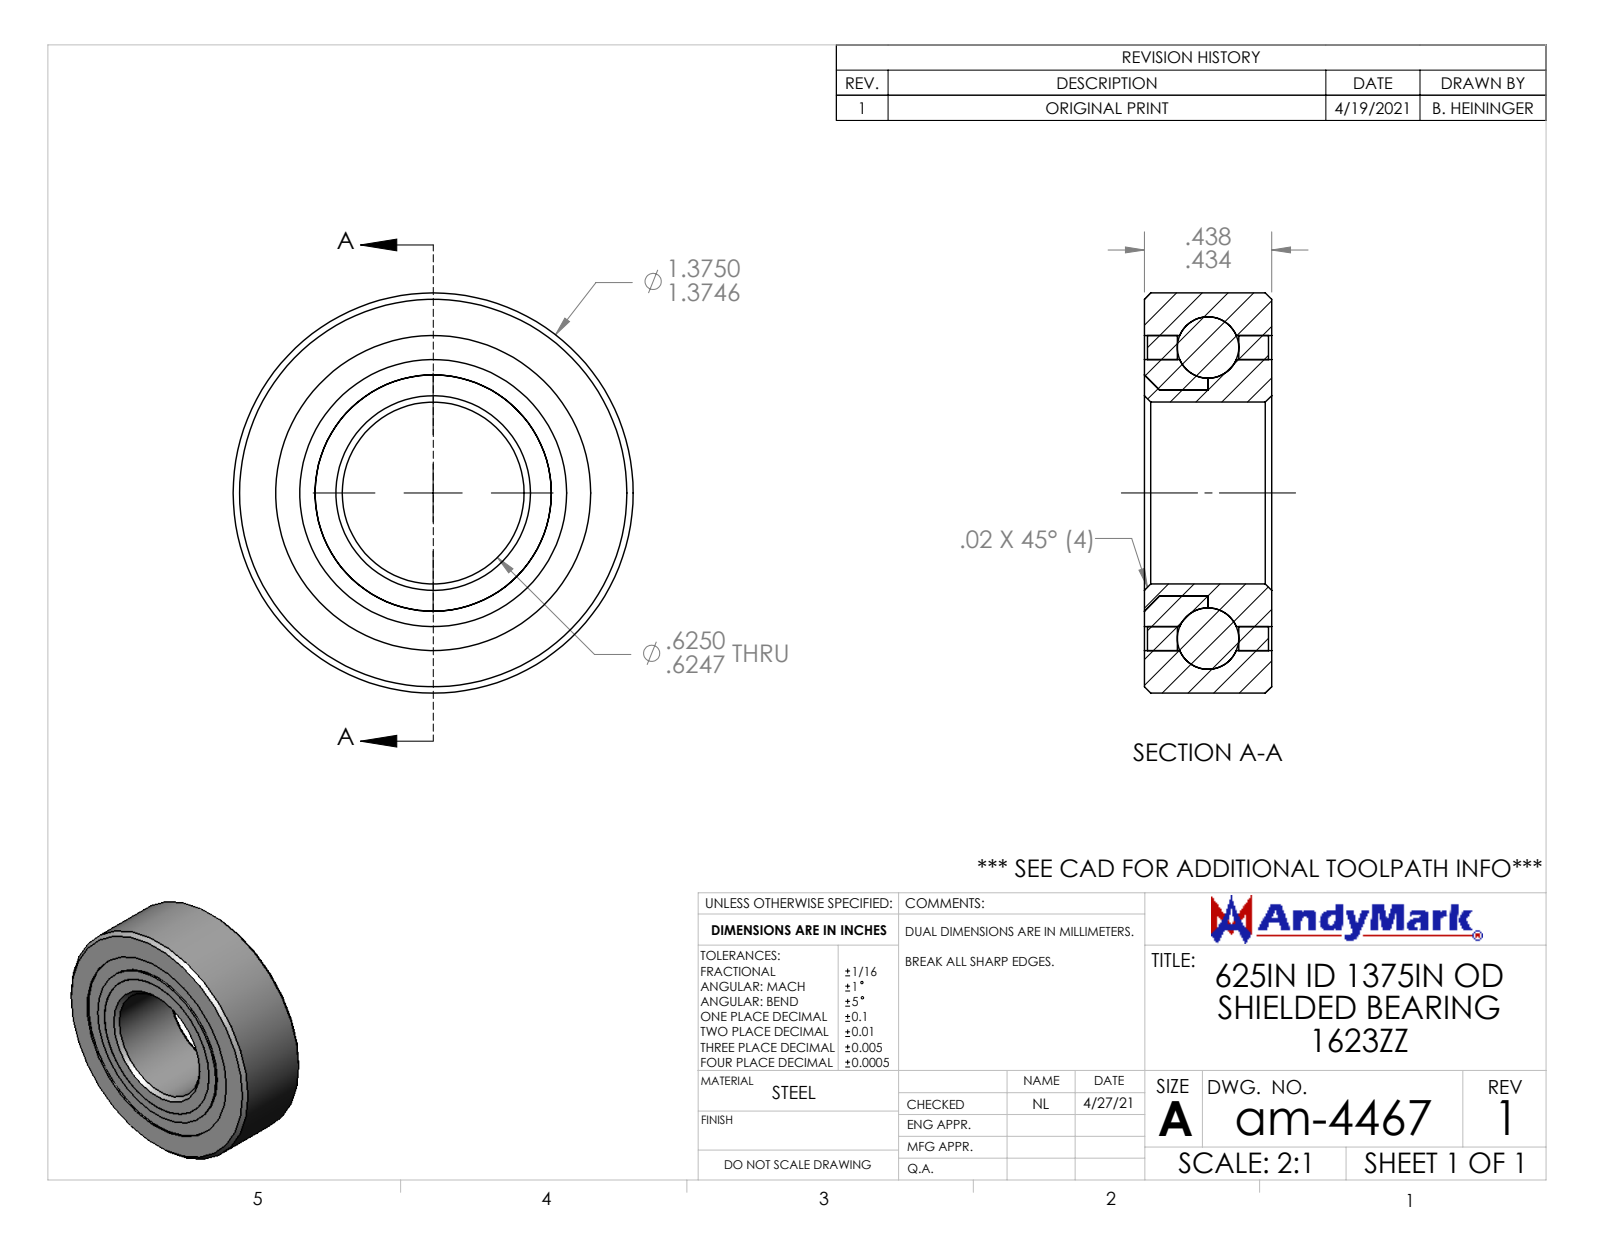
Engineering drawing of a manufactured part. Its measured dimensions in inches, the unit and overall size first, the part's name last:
Units: inches
Overall size (bounding box): 1.375 × 1.375 × 0.438
Round holes (diameter × count): ⌀0.625 ×1, ⌀0.707 ×1, ⌀0.918 ×1, ⌀1.082 ×1
Round bosses / shafts (diameter × count): ⌀1.375 ×1
Main face-to-face distances: 0.438, 0.427, 0.113, 0.324, 0.102, 0.313, 0.219, 0.208, 0.106, 0.416
Volume: 0.443 in³ · Surface area: 12.49 in²
Bodies: 15 solids, 73 faces (11 planar, 24 cylindrical, 38 other)
Part name (STEP PRODUCT): am-4467 1-2 in ID 1 3-8 in OD Shielded Bearing R1623ZZ
STEP written by: SolidWorks 2019 (AUTOMOTIVE_DESIGN)
